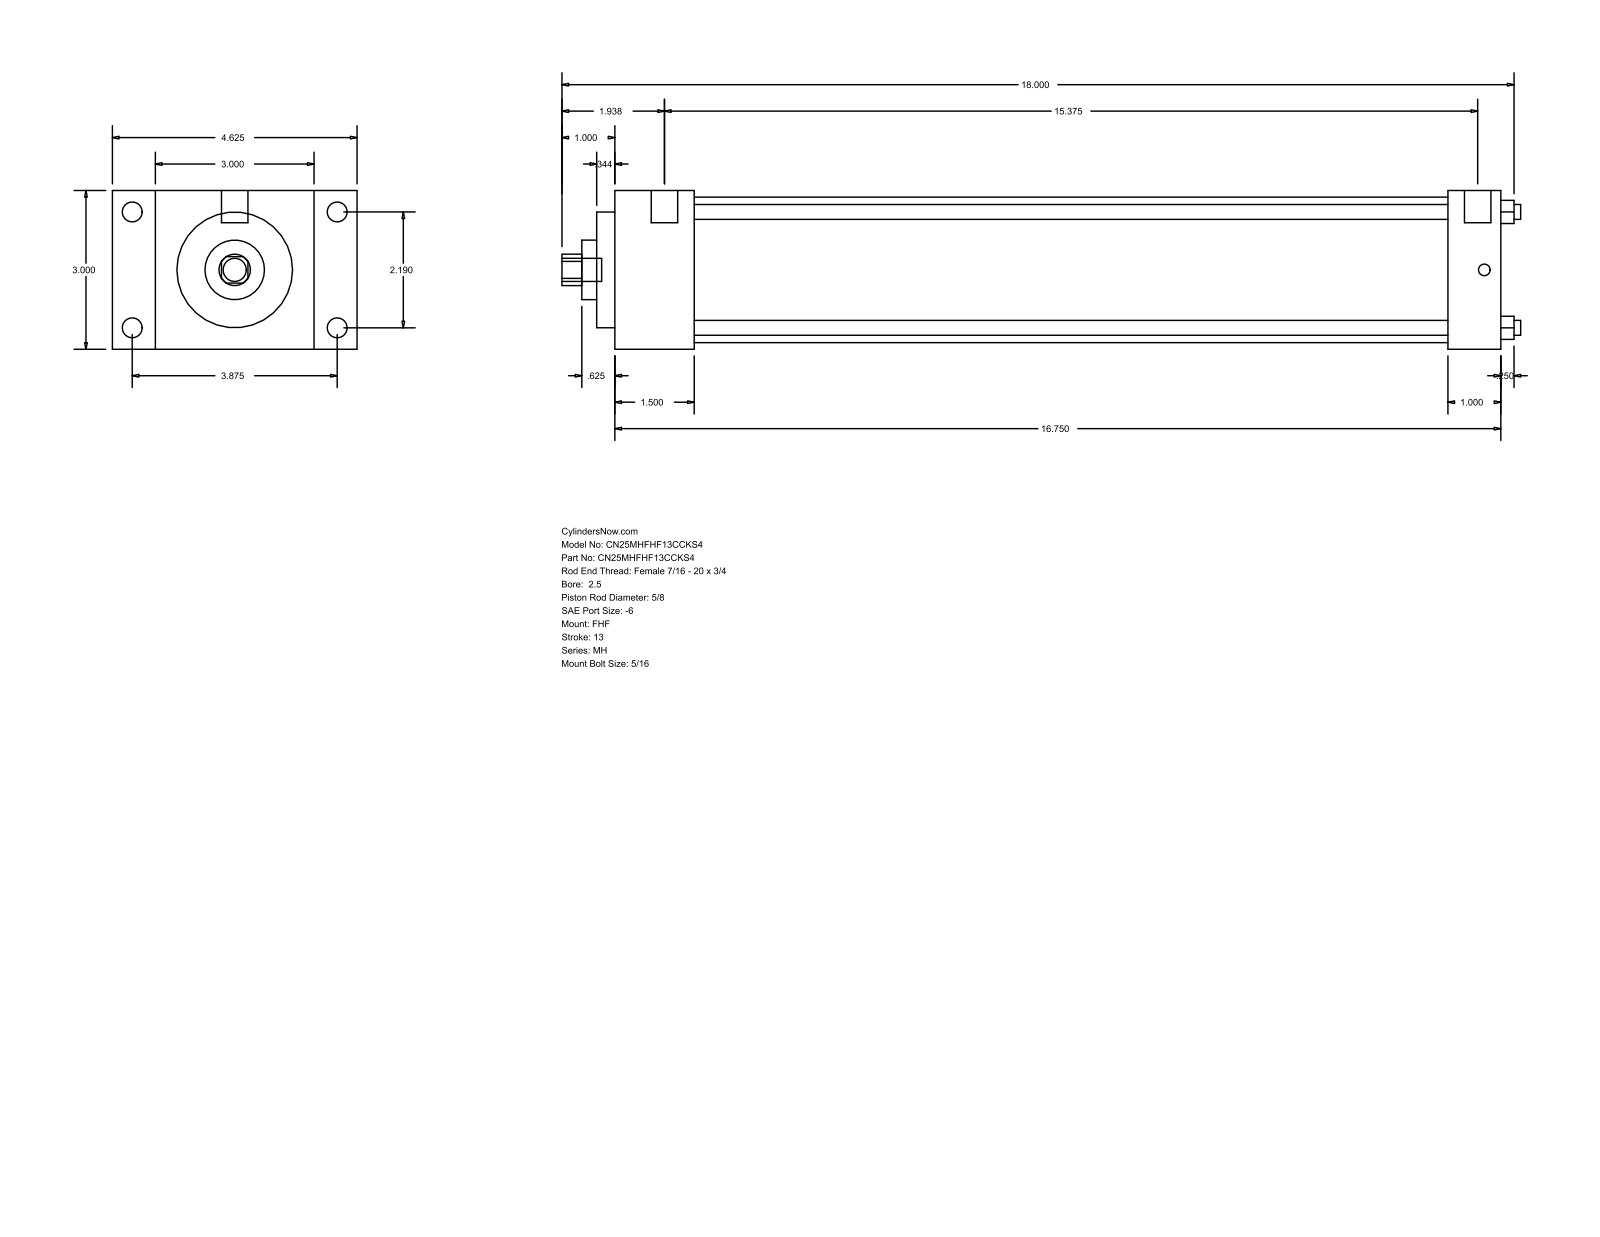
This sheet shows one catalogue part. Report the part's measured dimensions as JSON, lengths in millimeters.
{"part_name": "MH_FHF__0250_0.625", "step_written_by": "GSSL Pune (CONFIG_CONTROL_DESIGN)", "units": "millimeters", "bodies": {"solids": 0, "faces": 90, "planar": 61, "cylindrical": 29, "other": 0}, "overall_size": [460.38, 117.47, 76.2], "round_holes": [[7.14, 4], [15.88, 1], [28.57, 1], [55.55, 1], [69.85, 1]], "round_bosses_or_shafts": [[9.53, 4], [5.56, 4], [12.7, 2], [11.11, 1]], "partial_cylinders_radius": [[7.54, 1]], "face_to_face_distances": [76.2, 425.45, 38.1, 387.35, 20.64, 96.84, 117.48, 25.4, 400.05, 361.95], "hole_center_spacings": [39.33, 55.62, 78.66]}
